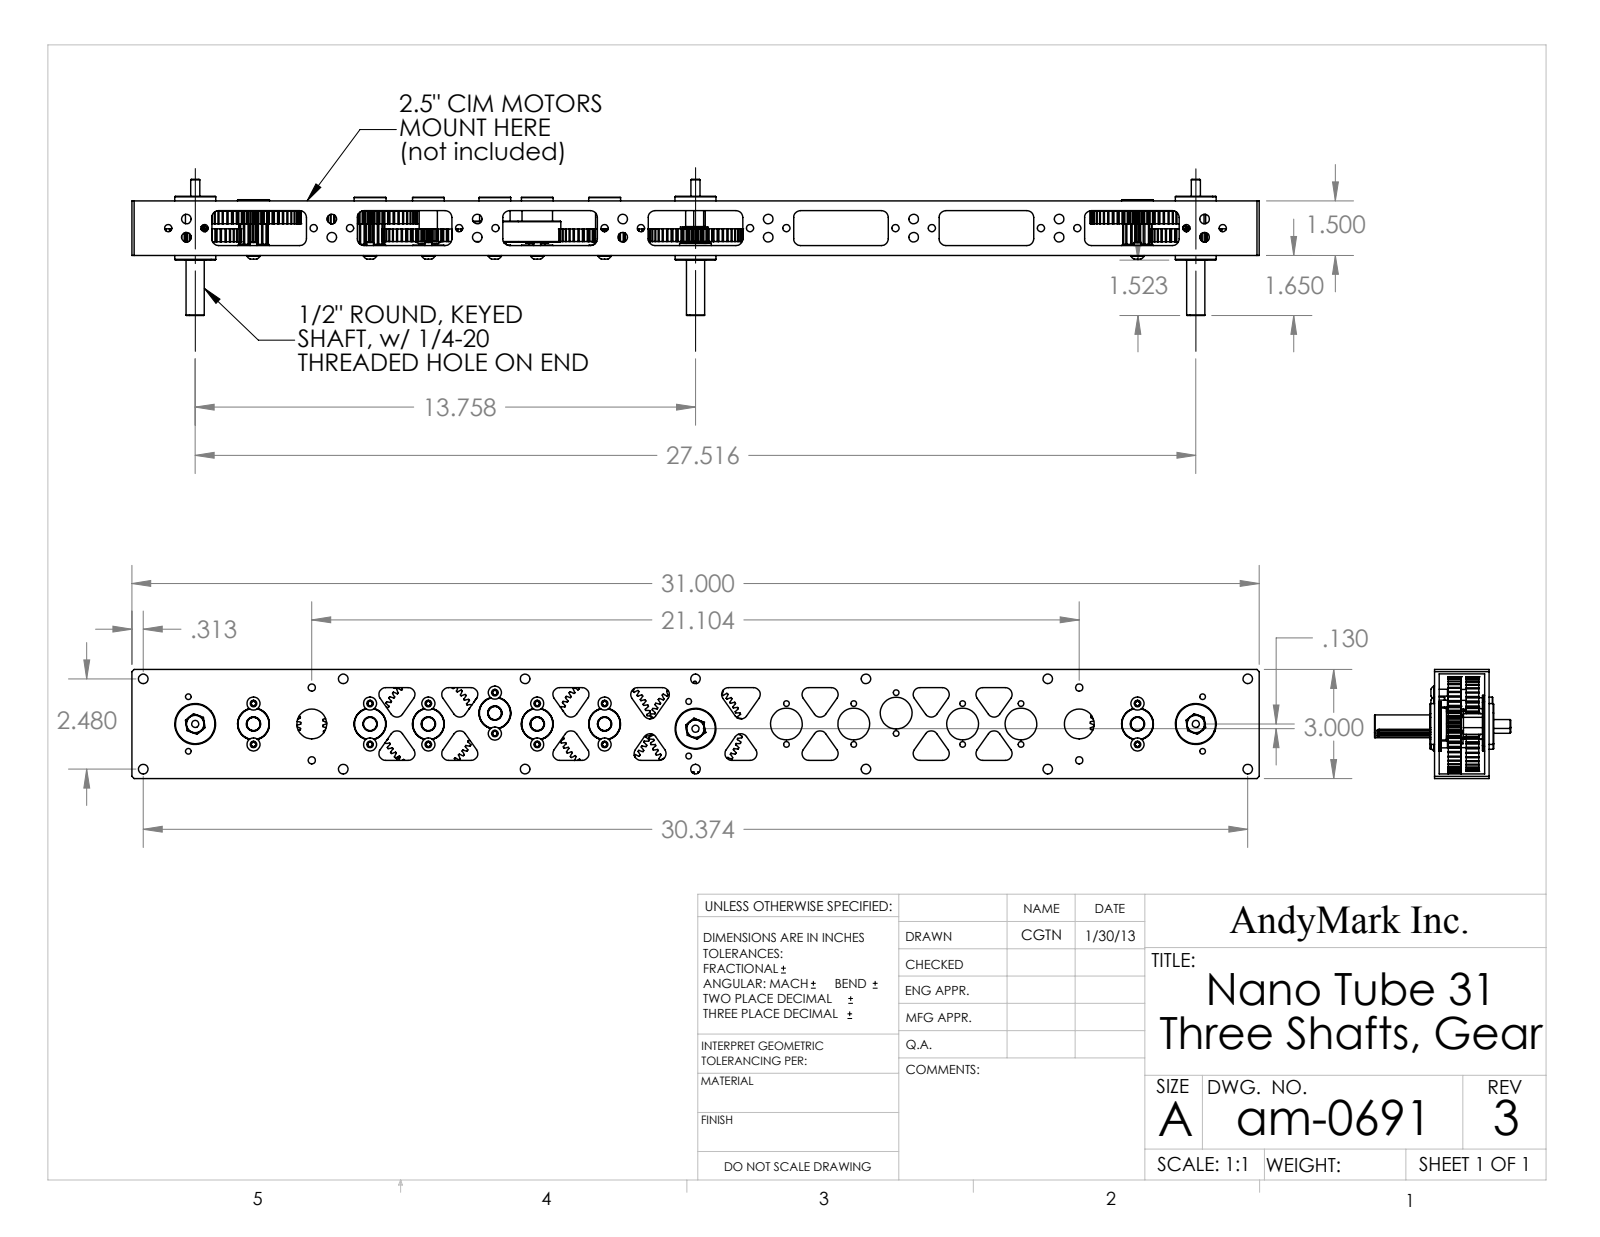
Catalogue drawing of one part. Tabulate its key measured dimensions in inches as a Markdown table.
| quantity | value |
| --- | --- |
| part name | am-0691 Nano Tube 31 - Three 500 Key Shafts - Gear Drive; am-0653 ToughBox Nano Tube 31 Rev3; Toughbox Nano d04; FR8ZZ Hex Bearing b (+8 more) |
| STEP written by | SolidWorks 2010 (CONFIG_CONTROL_DESIGN) |
| units | inches |
| bodies | 68 solids, 3915 faces (859 planar, 2688 cylindrical, 368 other) |
| overall size | 31 × 3.745 × 3 |
| volume | 45.32 in³ |
| surface area | 671.4 in² |
| round holes (diameter × count) | 0.156 × 30, 0.264 × 30, 0.2 × 16, 0.874 × 12, 0.375 × 7, 0.199 × 4, 0.196 × 3, 0.375 × 3, 0.593 × 3, 1.125 × 3, 0.16 × 2, 0.44 × 2 |
| round bosses / shafts (diameter × count) | 0.361 × 14, 0.19 × 14, 0.875 × 10, 0.972 × 7, 0.375 × 7, 0.875 × 5, 1.225 × 4, 1.1 × 4 |
| partial cylindrical surfaces (radius × count) | 0.6 × 800, 0.34 × 84, 0.187 × 72, 0.02 × 30, 0.008 × 18, 0.06 × 12, 1.187 × 8, 1.188 × 8 |
| main face-to-face distances | 0.125, 0.125, 1.5, 1.375, 1.25, 1.375, 3, 2.875, 2.75, 2.875 |
| hole center spacings | 0.559, 3.509, 4, 4.507, 7.504, 8, 8.504, 11.503 |
